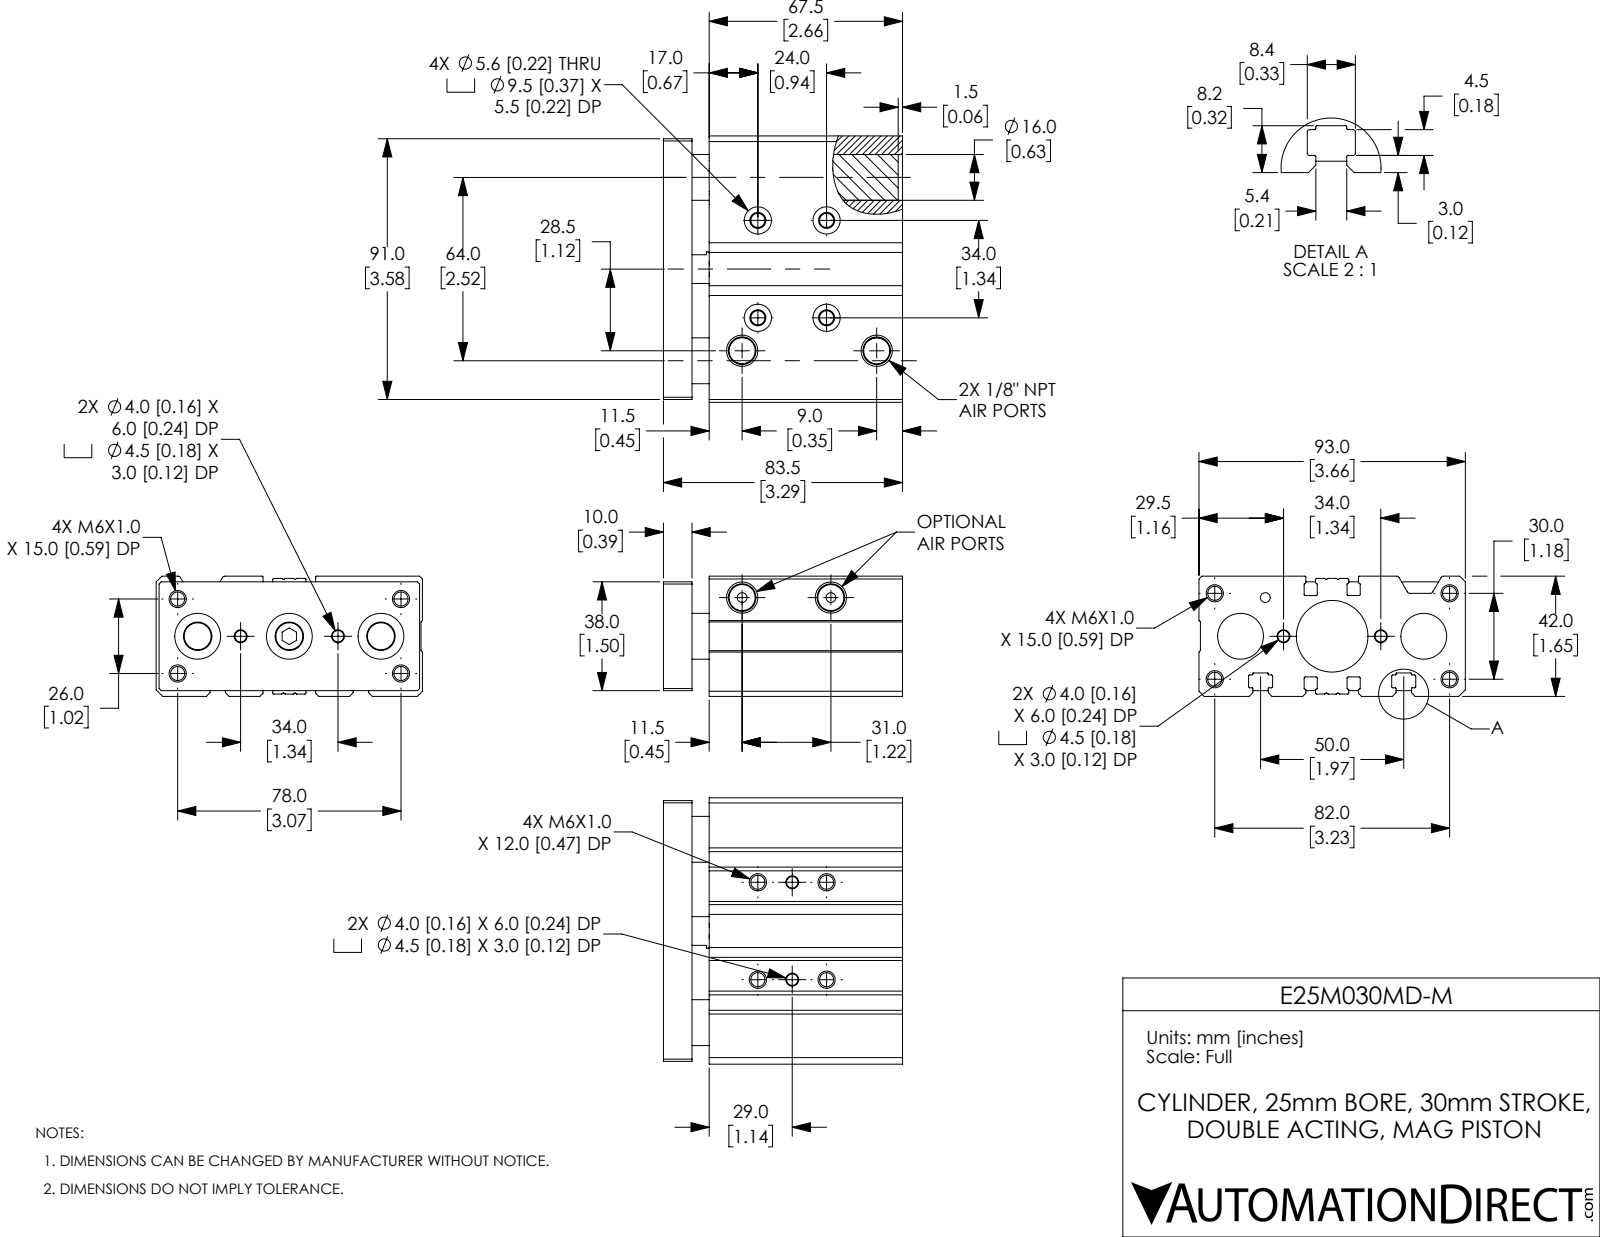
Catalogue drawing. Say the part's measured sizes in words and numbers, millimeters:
The part is named "E25M030MD-M_BODY; E25M030MD-M_ENDPLATE; E25M030MD-M". Its 3-D file was written by "SolidWorks 2019 (CONFIG_CONTROL_DESIGN)". It is 5 solids with 423 faces: 139 planar, 190 cylindrical and 94 other. Overall it measures 93 by 83.5 by 42 millimeters. Its volume is 253 932 cubic millimeters and its surface area 73 957 square millimeters. Round holes: 8 of diameter 4.92, 4 of diameter 4, 4 of diameter 4.5, 4 of diameter 4.92, 4 of diameter 5.6, 4 of diameter 9.5, 3 of diameter 3.43, 3 of diameter 8, 3 of diameter 16, 2 of diameter 9.91, 1 of diameter 16, 1 of diameter 25. Round bosses or shafts: 1 of diameter 12, 1 of diameter 9.91. Partial cylindrical surfaces (rounded edges, fillets, slot ends): 32 of radius 0.2, 28 of radius 0.4, 4 of radius 1, 2 of radius 0.3. The main face-to-face distances are 6, 42, 16, 10, 2, 83.5, 73.5, 67.5, 40, 93. The hole center spacings are 2.83, 12, 14.76, 17.49, 25.55, 28.07, 28.3, 34.
